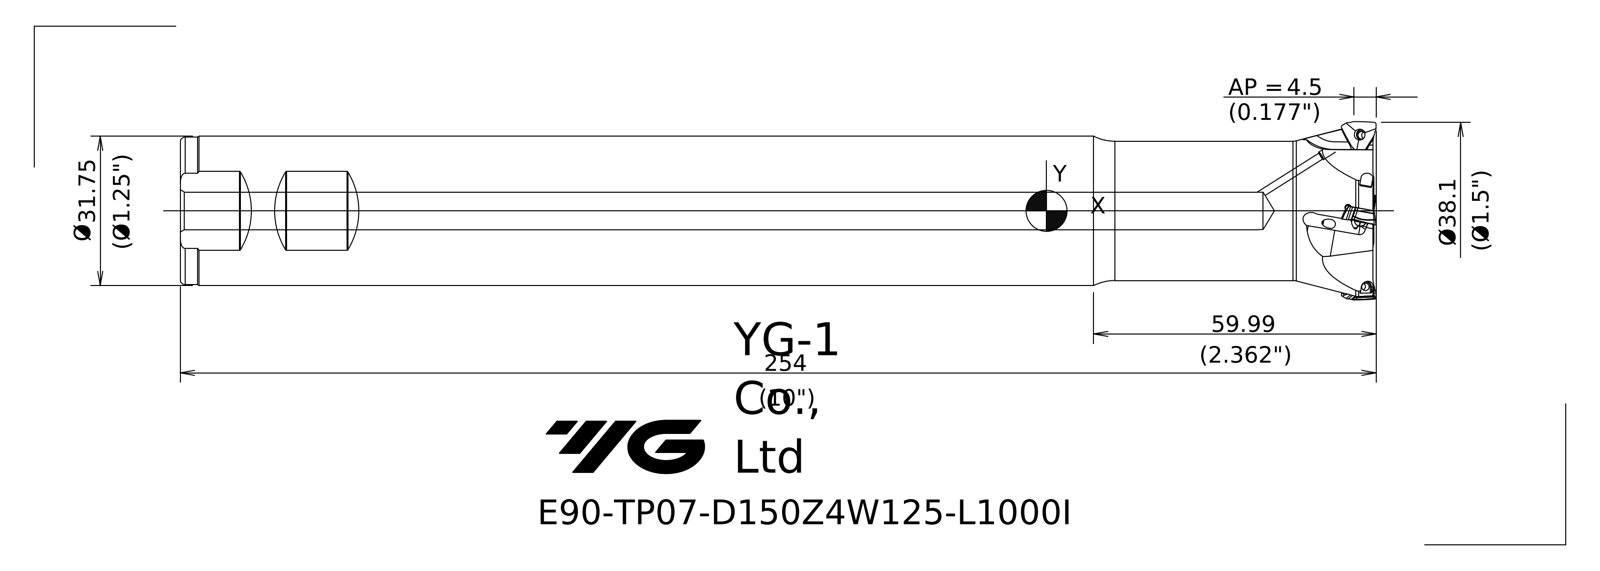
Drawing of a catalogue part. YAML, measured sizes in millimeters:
part_name: "102215A88E190eii"
step_written_by: "SIEMENS PLM Software NX 10.0 (AP203_CONFIGURATION_CONTROLLED_3D_DESIGN_OF_MECHANICAL_PARTS_AND_ASSEMBLIES_MIM_LF)"
units: millimeters
bodies: {solids: 1, faces: 51, planar: 8, cylindrical: 8, other: 35}
overall_size: [254, 38.16, 38.16]
volume: 185586
surface_area: 35035
round_holes:
  - {diameter: 1.5, count: 1}
  - {diameter: 8, count: 1}
round_bosses_or_shafts:
  - {diameter: 31.75, count: 1}
  - {diameter: 31.35, count: 1}
  - {diameter: 29.6, count: 1}
partial_cylinders:
  - {radius: 0.3, count: 3}
face_to_face_distances: [253.35, 253.5, 16.13]
